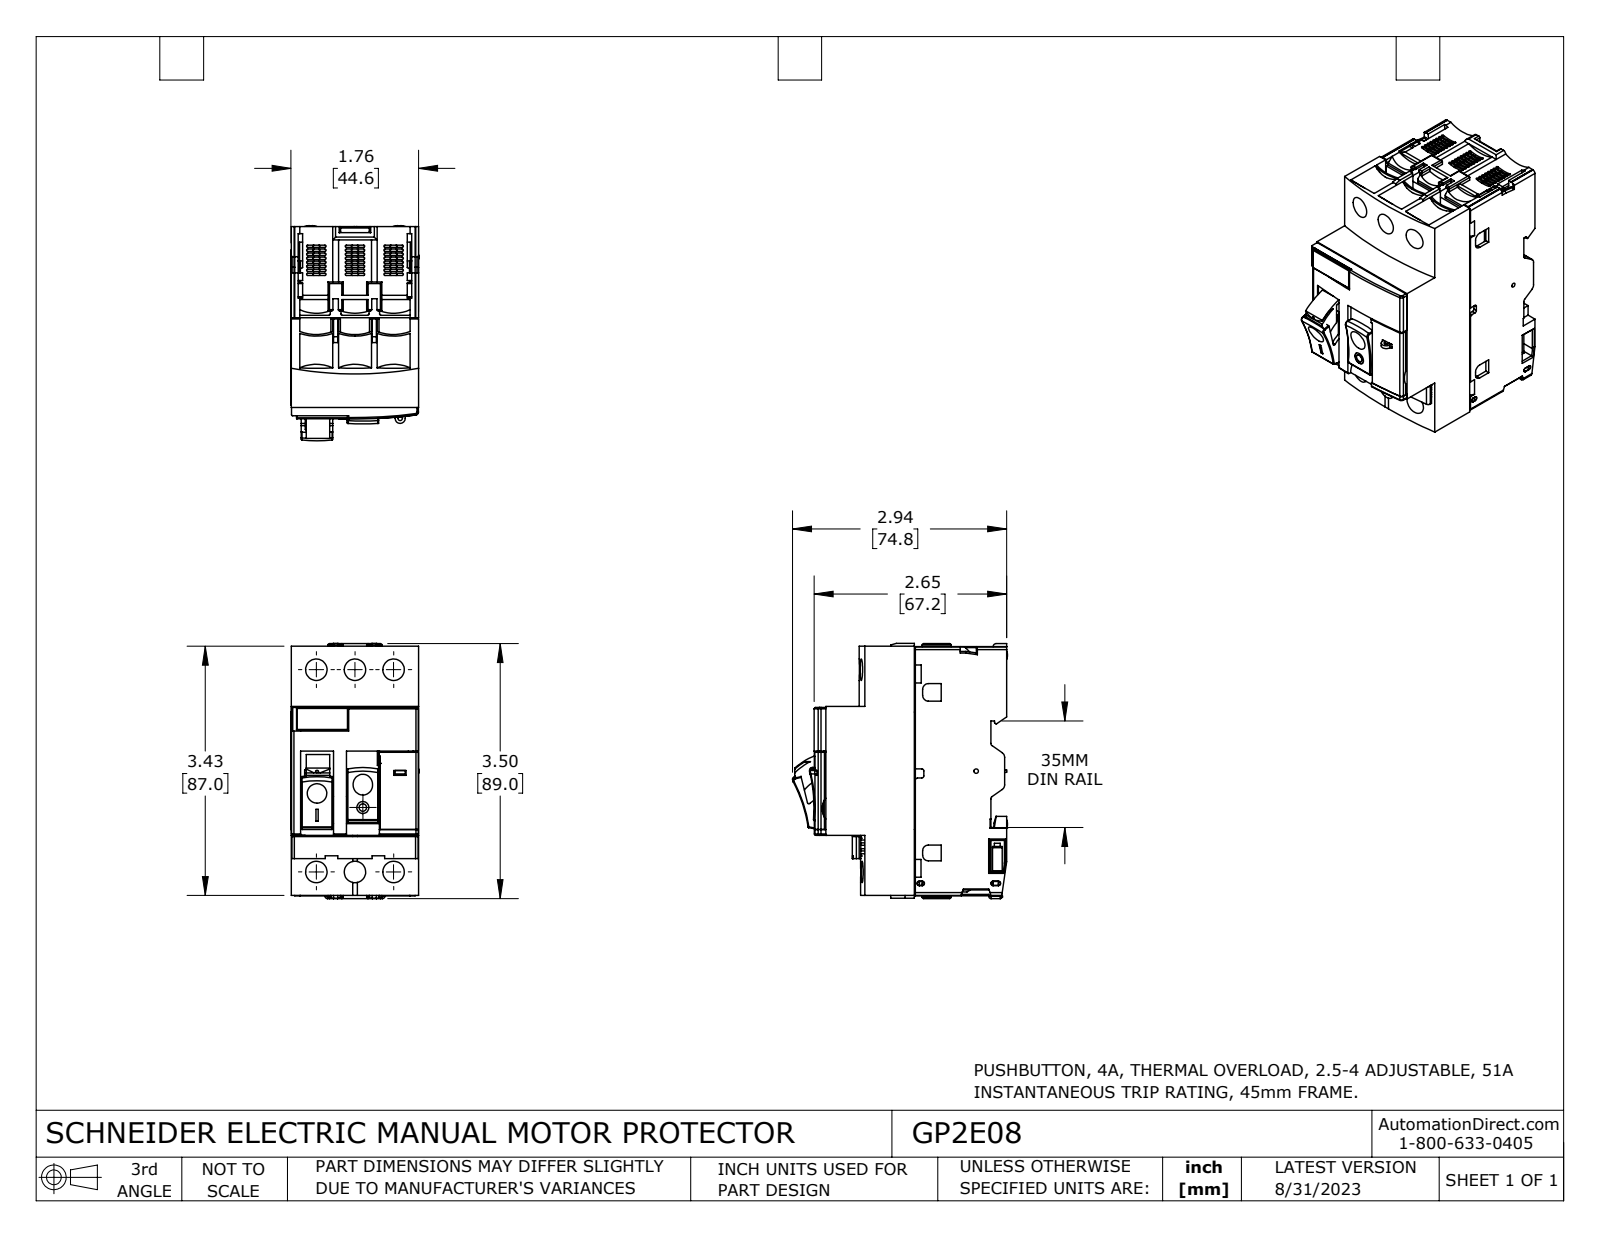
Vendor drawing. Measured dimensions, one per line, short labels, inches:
name: GP2E08
written by: SolidWorks 2021 (CONFIG_CONTROL_DESIGN)
unit: in
bodies: 15 solids, 2269 faces (1521 planar, 657 cylindrical, 91 other)
size: 3.508 × 2.957 × 1.764
volume: 11.58 in³; area: 98.93 in²
holes: 6× ⌀0.295, 5× ⌀0.197, 2× ⌀0.059, 1× ⌀0.157, 1× ⌀0.165, 1× ⌀0.315, 1× ⌀0.327, 1× ⌀0.335, 1× ⌀0.343
bosses: 2× ⌀0.244, 2× ⌀0.118, 1× ⌀0.382, 1× ⌀0.102, 1× ⌀0.047
rounds: 104× R0.016, 47× R0.02, 16× R0.039, 12× R0.01, 12× R0.012, 12× R0.031, 8× R0.059, 6× R0.004
face distances: 1.752, 0.531, 0.115, 1.233, 1.756, 0.059, 1.637, 0.581, 1.053, 1.171
hole spacings: 0.531, 2.83, 2.779, 0.346, 0.402, 0.546, 0.671, 0.726
